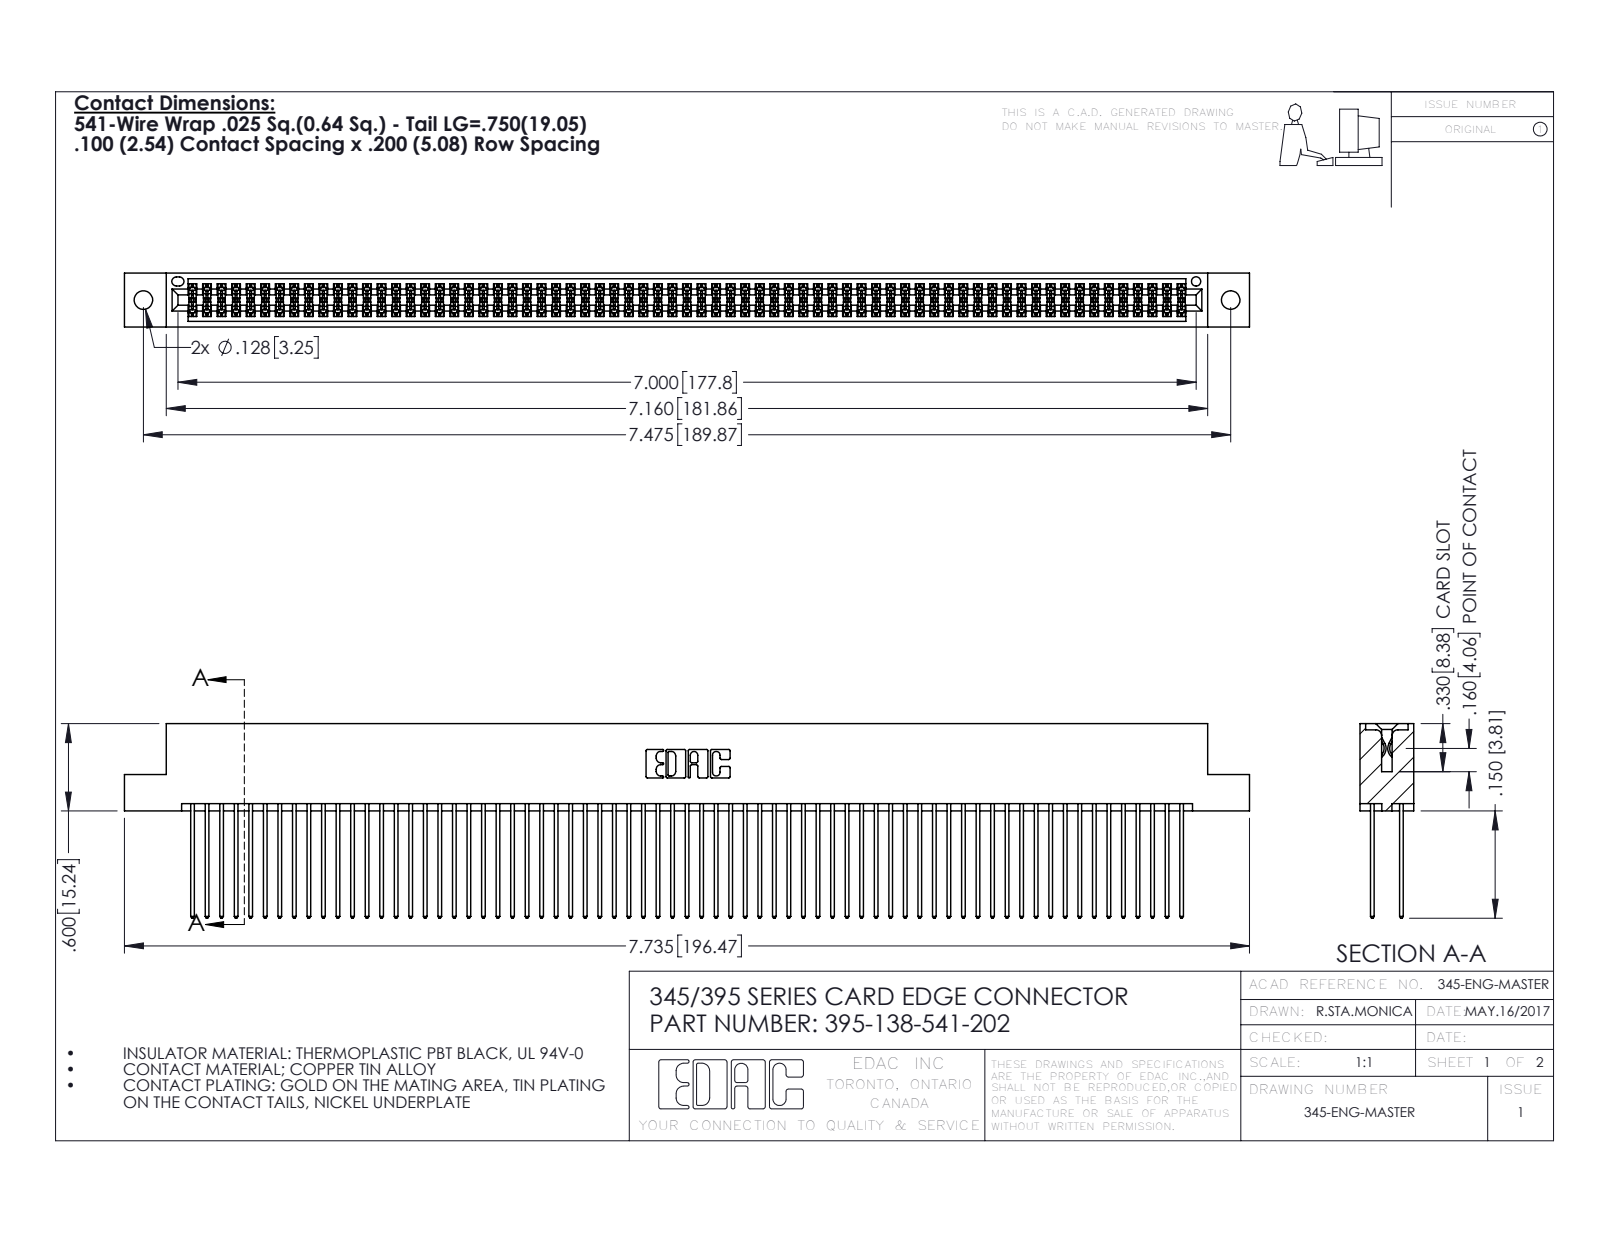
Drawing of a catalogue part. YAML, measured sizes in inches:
part_name: "345-292-001_345-293-141; 345 Part_Flush Mounting Lugs - 0.128 Dia; 395-138-541-202"
step_written_by: "SolidWorks 2016 (CONFIG_CONTROL_DESIGN)"
units: inches
bodies: {solids: 139, faces: 7026, planar: 4634, cylindrical: 2392, other: 0}
overall_size: [7.735, 1.337, 0.37]
volume: 1.226
surface_area: 52.19
round_holes:
  - {diameter: 0.128, count: 2}
  - {diameter: 0.064, count: 1}
partial_cylinders:
  - {radius: 0.006, count: 207}
  - {radius: 0.01, count: 138}
  - {radius: 0.01, count: 22}
  - {radius: 0.007, count: 6}
  - {radius: 0.031, count: 6}
  - {radius: 0.026, count: 3}
  - {radius: 0.014, count: 2}
  - {radius: 0.019, count: 2}
face_to_face_distances: [0.298, 0.072, 0.2, 0.098, 0.272, 0.025, 0.225, 0.37, 0.175, 0.149]
hole_center_spacings: [0.27, 7.239, 7.475]
